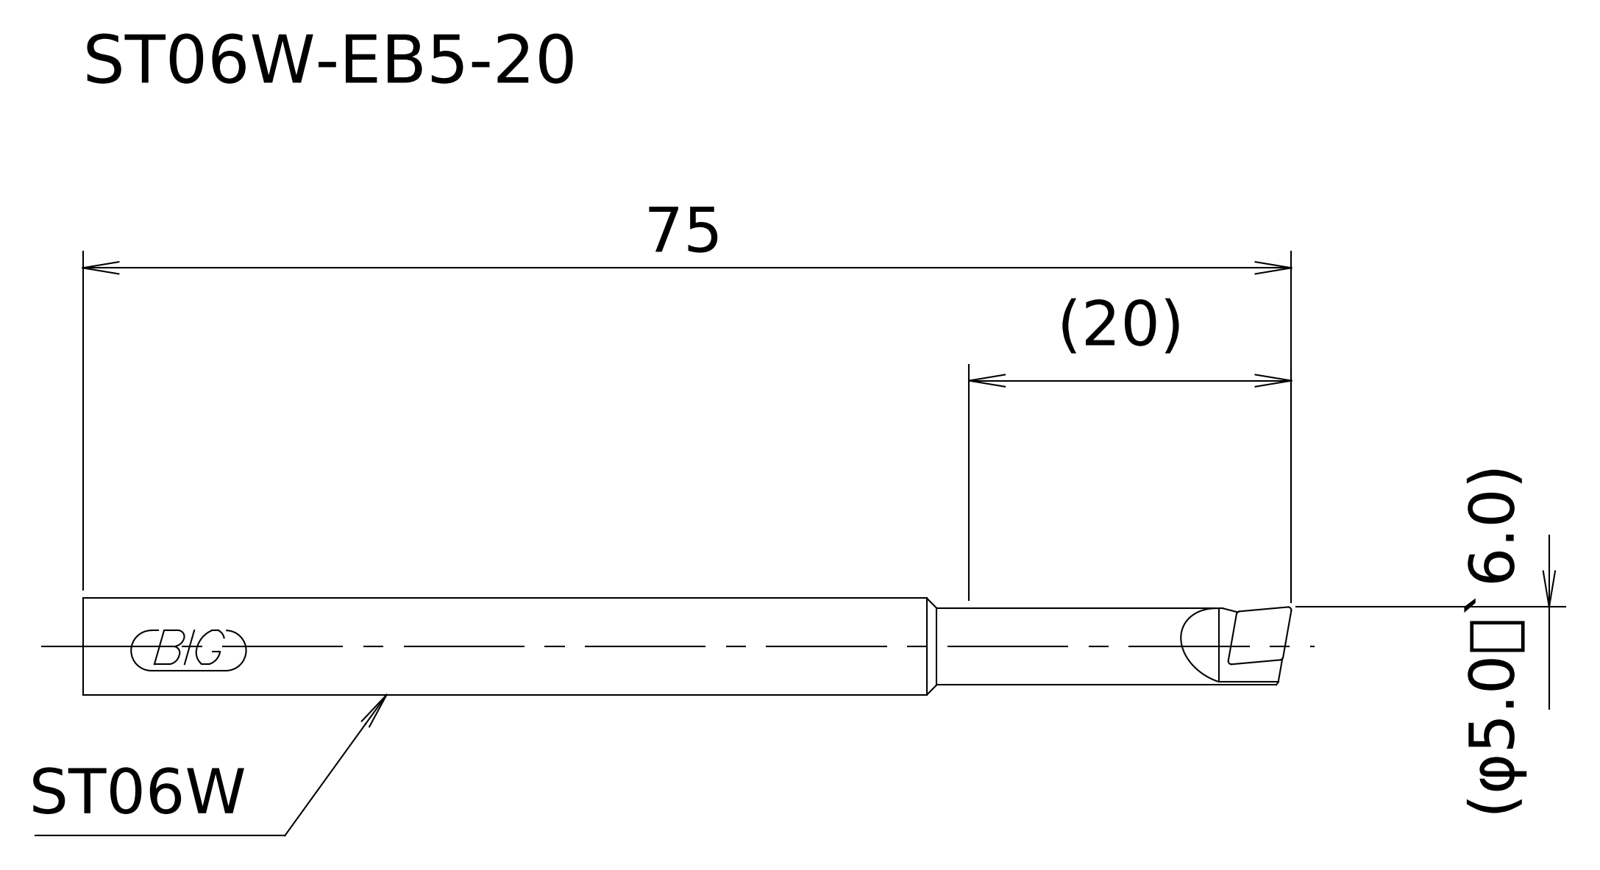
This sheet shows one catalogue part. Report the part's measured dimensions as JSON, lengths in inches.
{"part_name": "240[2]", "step_written_by": "Kubotek KeyCreator 2011 V10.0.2 (22737) (automotive_design)", "units": "inches", "bodies": {"solids": 2, "faces": 31, "planar": 18, "cylindrical": 6, "other": 7}, "overall_size": [2.953, 0.236, 0.236], "volume_in3": 0.112, "surface_area_in2": 2.161, "round_holes": [[0.063, 1], [0.071, 1]], "round_bosses_or_shafts": [[0.236, 1], [0.187, 1]], "partial_cylinders_radius": [[0.01, 2]], "face_to_face_distances": [0.045, 0.039, 0.044, 0.05, 0.02]}
